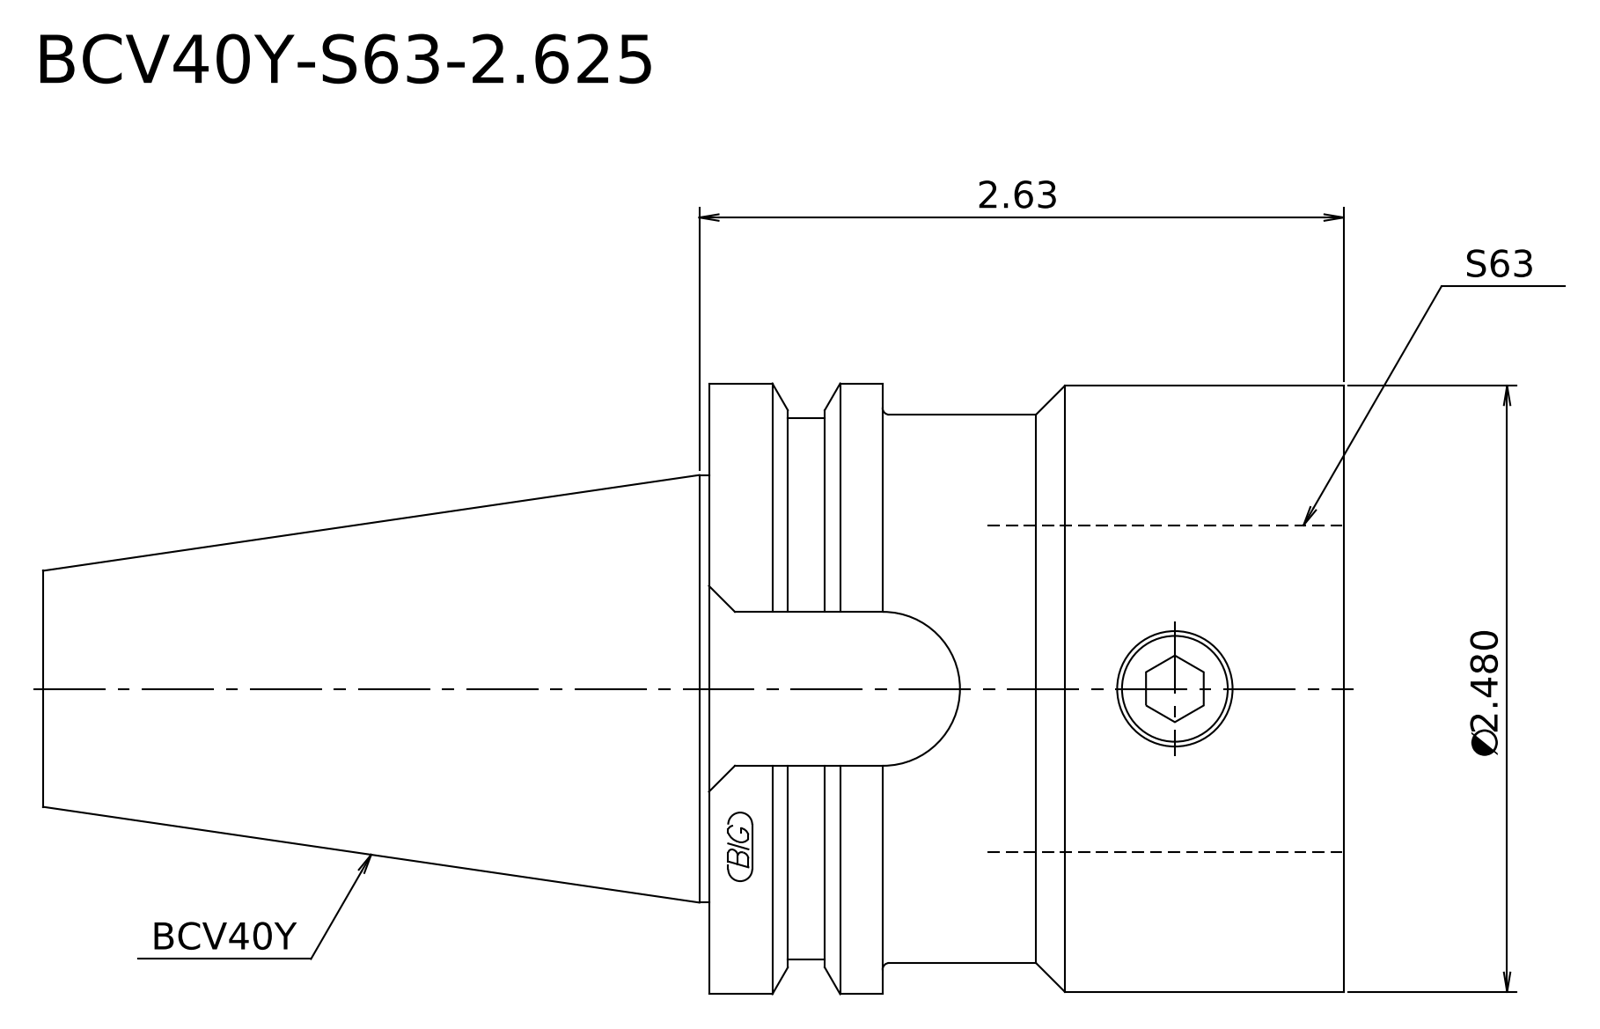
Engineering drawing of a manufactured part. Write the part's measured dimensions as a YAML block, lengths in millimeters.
step_written_by: "Kubotek KeyCreator 2011 V10.0.2 (22737) (automotive_design)"
units: millimeters
bodies: {solids: 1, faces: 16, planar: 6, cylindrical: 6, other: 4}
overall_size: [135.25, 63.5, 63.5]
volume: 260418
surface_area: 27213
round_bosses_or_shafts:
  - {diameter: 63.5, count: 1}
  - {diameter: 63, count: 1}
  - {diameter: 57, count: 1}
  - {diameter: 56.36, count: 1}
  - {diameter: 44.45, count: 1}
face_to_face_distances: [66, 47.95, 18.05, 135.25, 87.3, 69.25, 53.96, 6.01, 12.04, 81.29]
